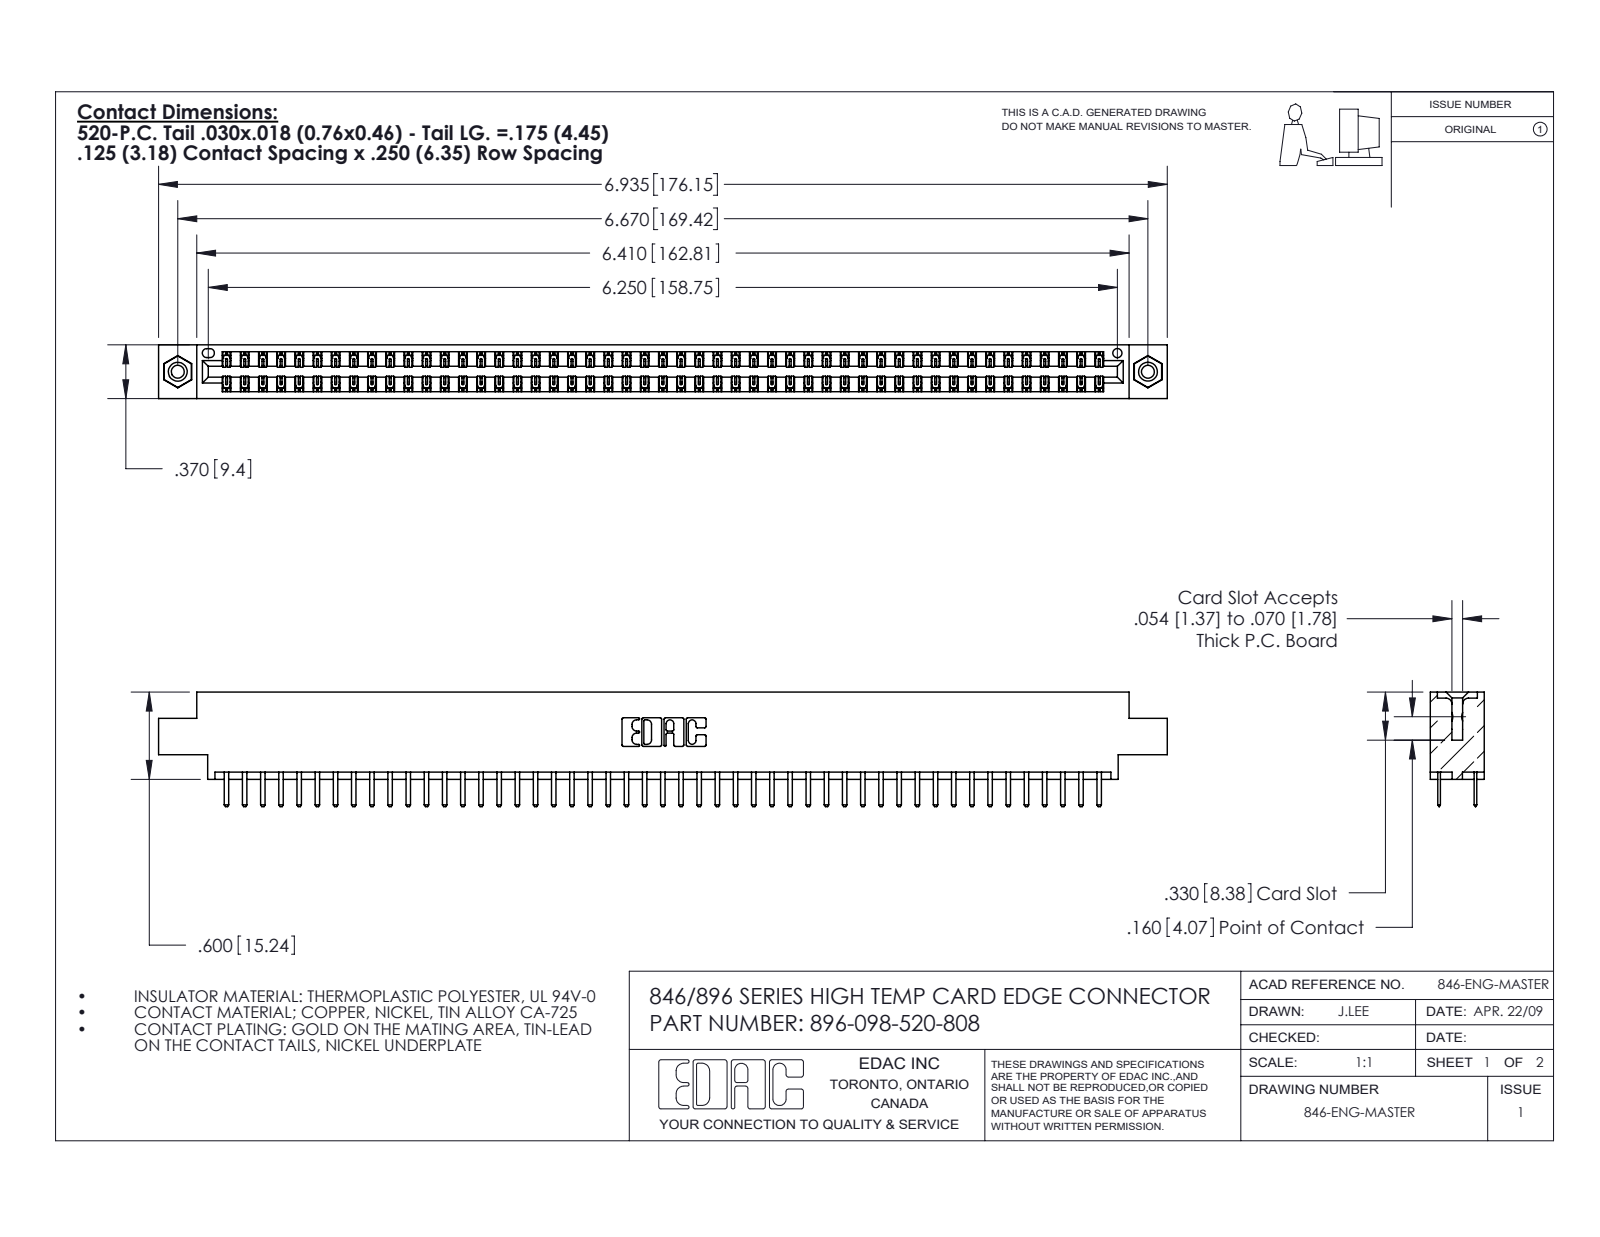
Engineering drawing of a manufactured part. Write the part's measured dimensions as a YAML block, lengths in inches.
part_name: "345-292-001_345-293-120; 396-098-520-808; 345-250-001_345-250-003-102; 346 Part_0.170 Offset - 0.156 Dia-TI"
step_written_by: "SolidWorks 2016 (CONFIG_CONTROL_DESIGN)"
units: inches
bodies: {solids: 101, faces: 5674, planar: 3738, cylindrical: 1920, other: 16}
overall_size: [6.935, 0.788, 0.37]
volume: 1.039
surface_area: 36.6
round_holes:
  - {diameter: 0.089, count: 2}
  - {diameter: 0.125, count: 2}
  - {diameter: 0.156, count: 2}
  - {diameter: 0.064, count: 1}
round_bosses_or_shafts:
  - {diameter: 0.155, count: 2}
partial_cylinders:
  - {radius: 0.006, count: 147}
  - {radius: 0.01, count: 102}
  - {radius: 0.01, count: 22}
  - {radius: 0.007, count: 6}
  - {radius: 0.031, count: 6}
  - {radius: 0.026, count: 3}
  - {radius: 0.014, count: 2}
  - {radius: 0.022, count: 2}
face_to_face_distances: [0.048, 0.322, 0.25, 0.37, 0.275, 0.072, 0.298, 0.025, 0.222, 0.148]
hole_center_spacings: [0.246, 6.461, 6.67]
